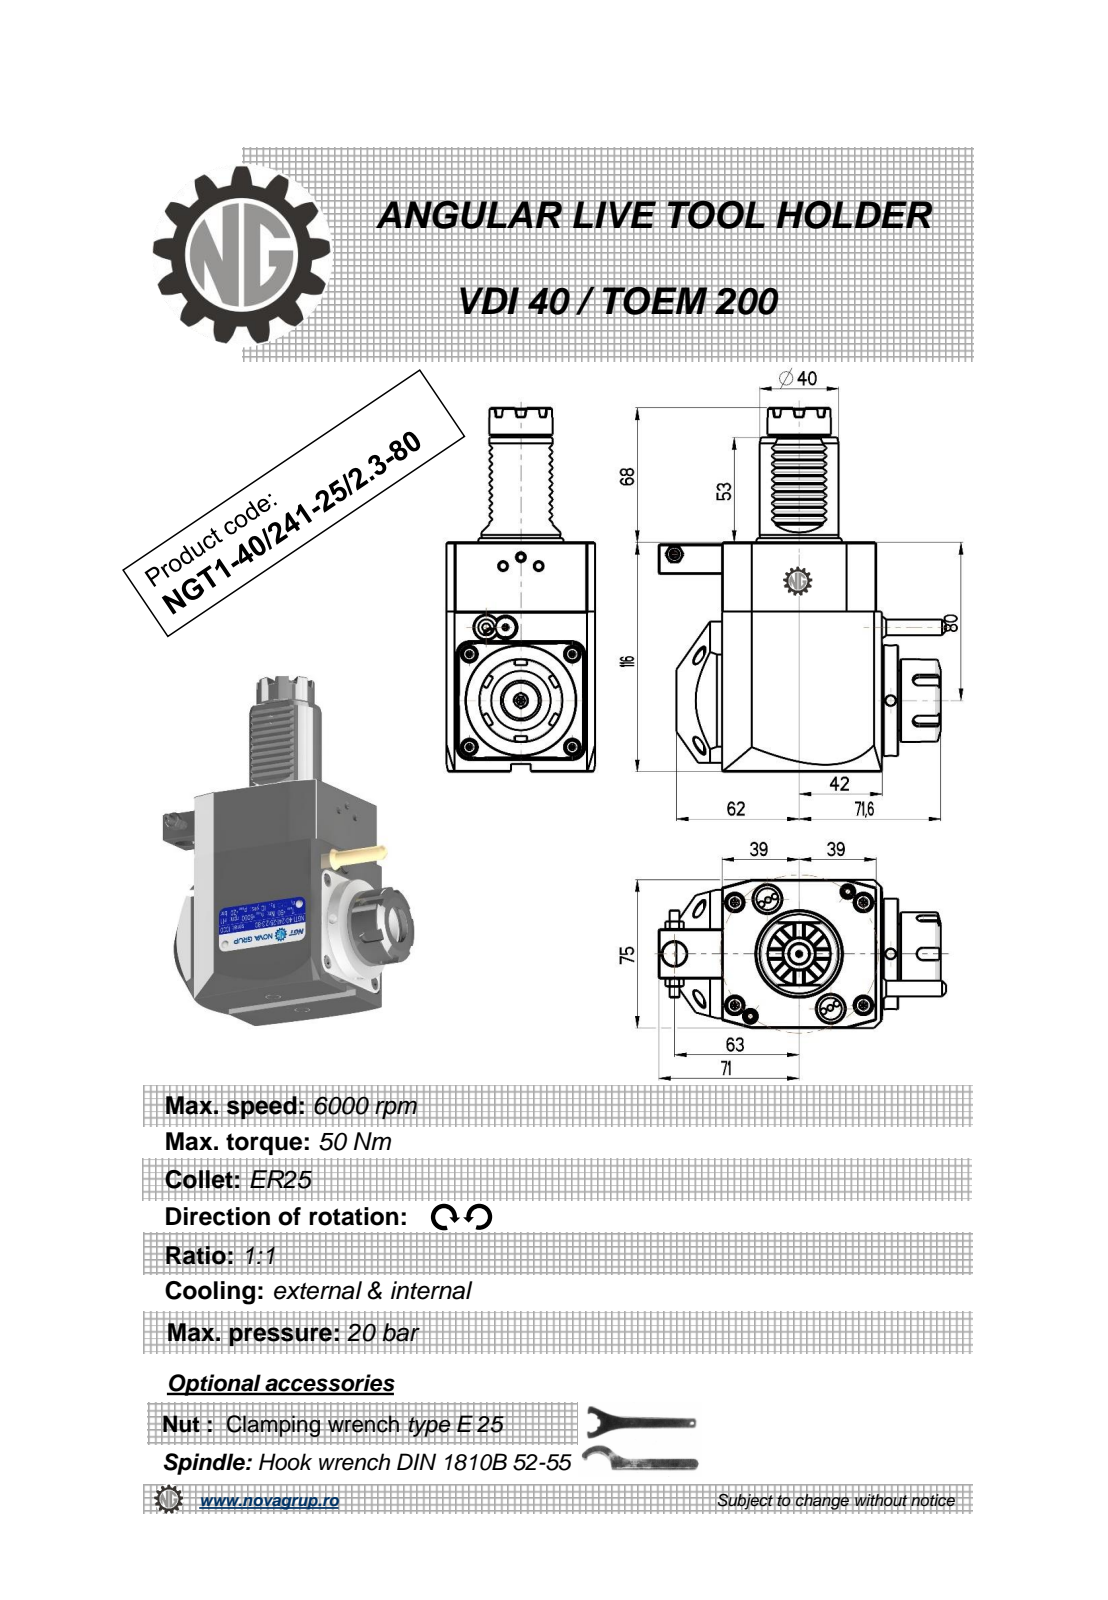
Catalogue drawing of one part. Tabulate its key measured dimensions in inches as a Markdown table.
| quantity | value |
| --- | --- |
| part name | NGT1_40_241_25_2_3_80 |
| STEP written by | PRO/ENGINEER BY PARAMETRIC TECHNOLOGY CORPORATION, 2010280 (CONFIG_CONTROL_DESIGN) |
| units | inches |
| bodies | 1 solid, 547 faces (263 planar, 94 cylindrical, 190 other) |
| overall size | 7.244 × 5.714 × 2.953 |
| volume | 53.31 in³ |
| surface area | 111.8 in² |
| round holes (diameter × count) | 0.197 × 3, 0.118 × 1, 0.165 × 1, 0.374 × 1, 0.472 × 1, 0.799 × 1 |
| round bosses / shafts (diameter × count) | 2.205 × 1, 1.693 × 1, 1.654 × 1, 1.575 × 1, 1.299 × 1, 1.26 × 1, 0.677 × 1, 0.394 × 1 |
| partial cylindrical surfaces (radius × count) | 0.012 × 20, 0.01 × 12, 0.008 × 6, 0.118 × 5, 1.575 × 1 |
| main face-to-face distances | 2.953, 4.567, 3.071, 3.189, 0.118, 0.433, 3.504, 0.315, 3.181, 0.11 |
| hole center spacings | 1.558, 1.611, 2.854, 4.301, 5.195 |
